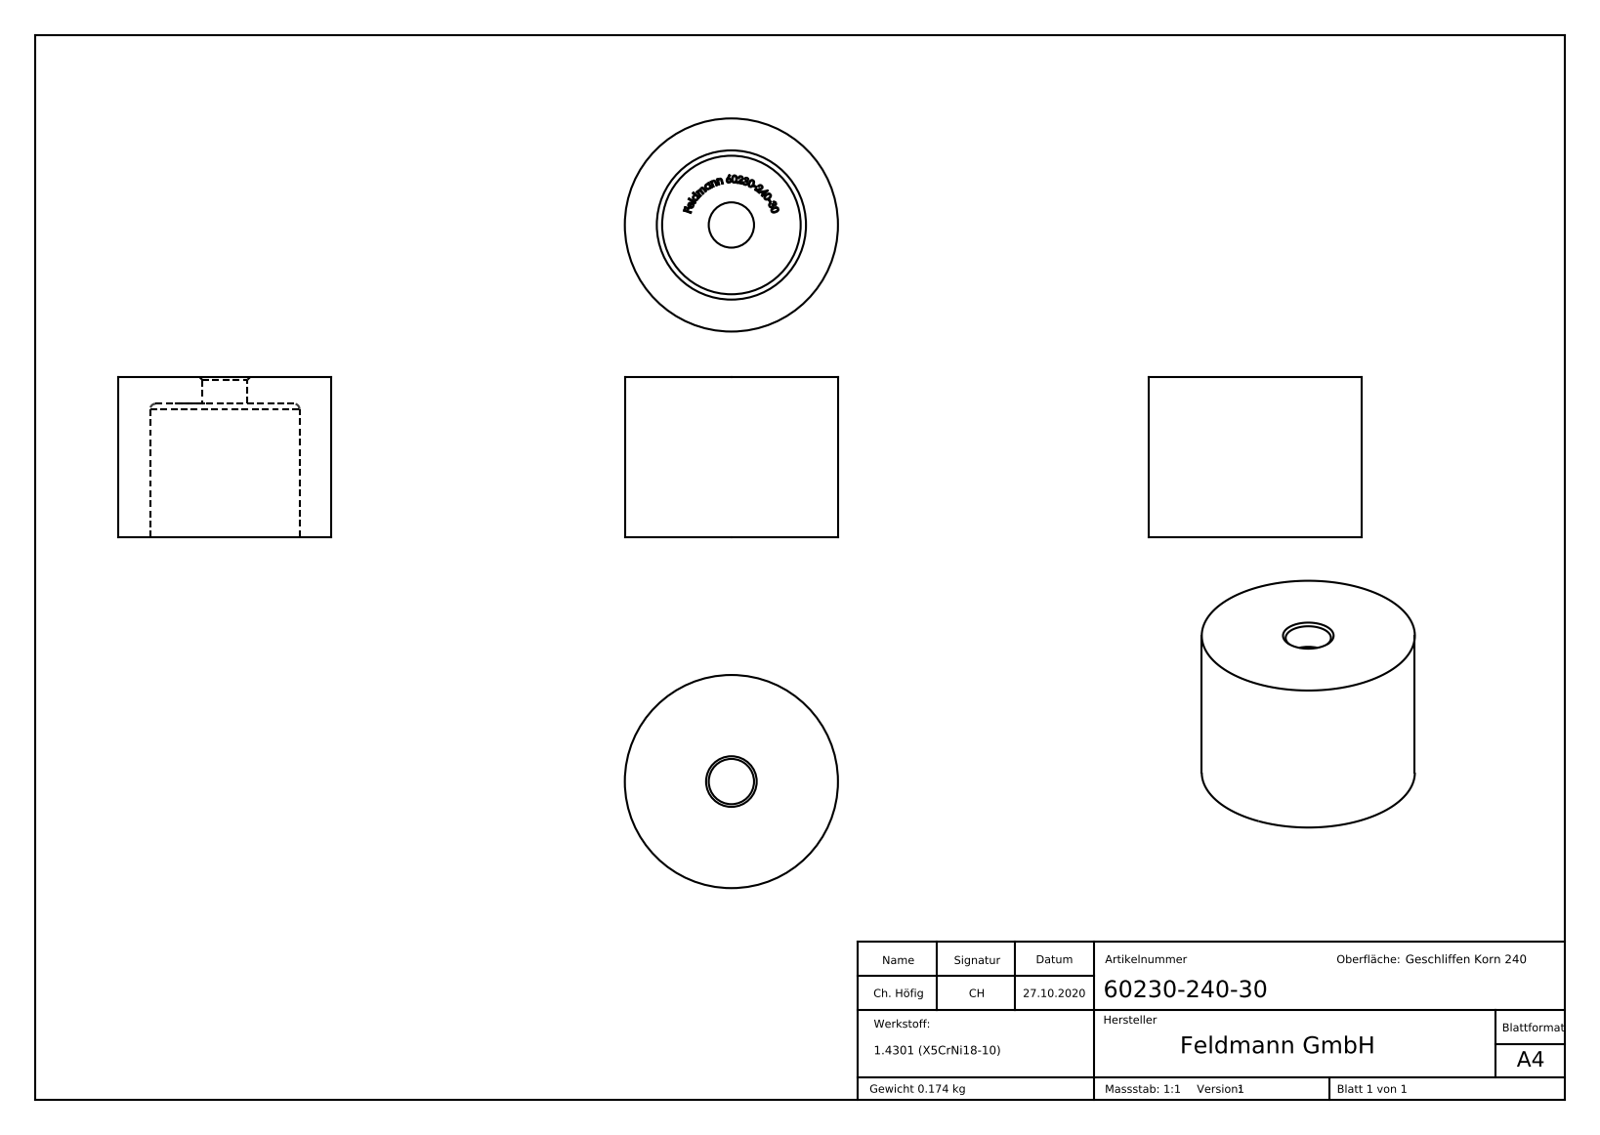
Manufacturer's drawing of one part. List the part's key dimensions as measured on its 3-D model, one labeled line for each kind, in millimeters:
Part name (STEP PRODUCT): 60230-240-30
STEP written by: SolidWorks 2018 (CONFIG_CONTROL_DESIGN)
Units: millimetres
Bodies: 1 solid, 271 faces (128 planar, 6 cylindrical, 137 other)
Overall size (bounding box): 40 × 40 × 30
Volume: 22 036 mm³ · Surface area: 8 468 mm²
Round holes (diameter × count): ⌀8.5 ×1, ⌀28 ×1
Round bosses / shafts (diameter × count): ⌀40 ×1
Main face-to-face distances: 30, 25, 5, 25.1, 4.9, 0.54, 0.66, 0.67, 0.72, 0.79
